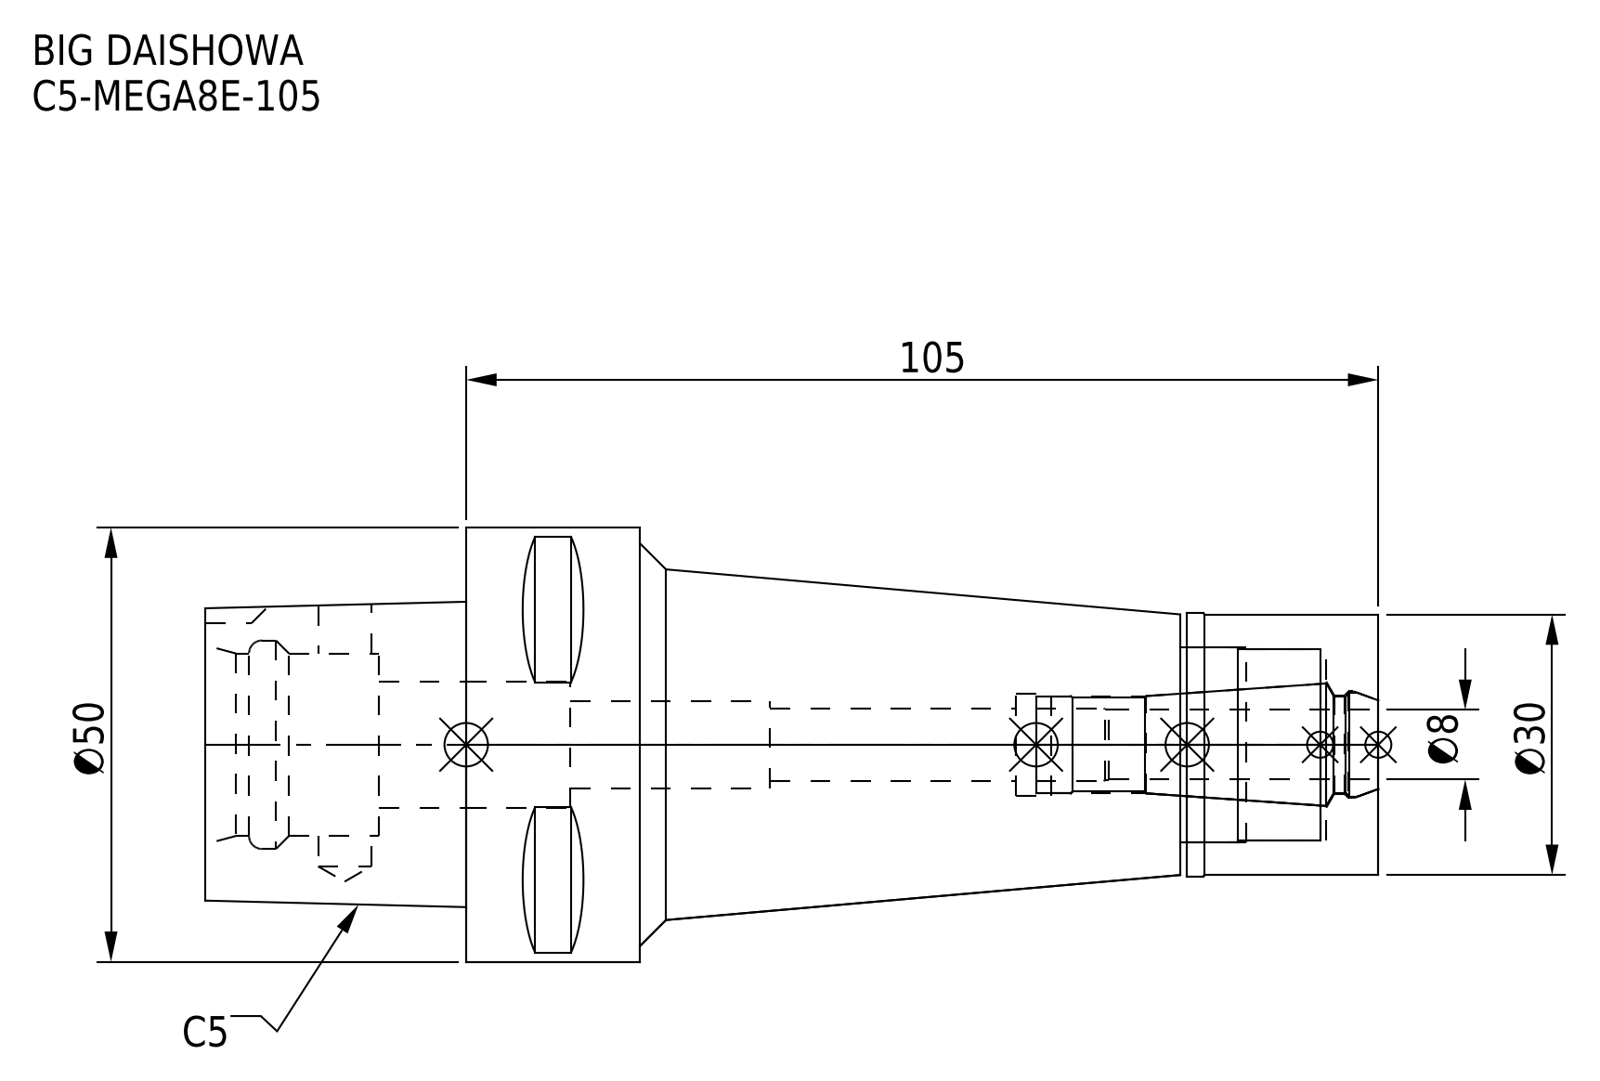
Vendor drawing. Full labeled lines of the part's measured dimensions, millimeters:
Part name (STEP PRODUCT): C5-MEGA8E-105-080_ASM.stp; C5-MEGA8E-105_1.stp; DXF_TEMP_ASSY_ASM_4_ASM.stp; C5-MEGA8E-105 (+3 more)
STEP written by: SolidWorks 2019 (CONFIG_CONTROL_DESIGN)
Units: millimetres
Bodies: 2 solids, 100 faces (37 planar, 39 cylindrical, 24 other)
Overall size (bounding box): 135 × 50 × 50
Volume: 124 455 mm³ · Surface area: 27 562 mm²
Round holes (diameter × count): ⌀6.1 ×1, ⌀8.4 ×1, ⌀10 ×1, ⌀11.2 ×1, ⌀11.4 ×1, ⌀11.8 ×1, ⌀12.3 ×1, ⌀14.5 ×1, ⌀21 ×1, ⌀22 ×1, ⌀22.5 ×1, ⌀24 ×1
Round bosses / shafts (diameter × count): ⌀50 ×1, ⌀30.3 ×1, ⌀30 ×1
Partial cylindrical surfaces — rounded edges, fillets, slot ends (radius × count): R4 ×1
Main face-to-face distances: 105, 30, 20, 22, 135, 83, 113, 22.8, 0.8, 82.2
